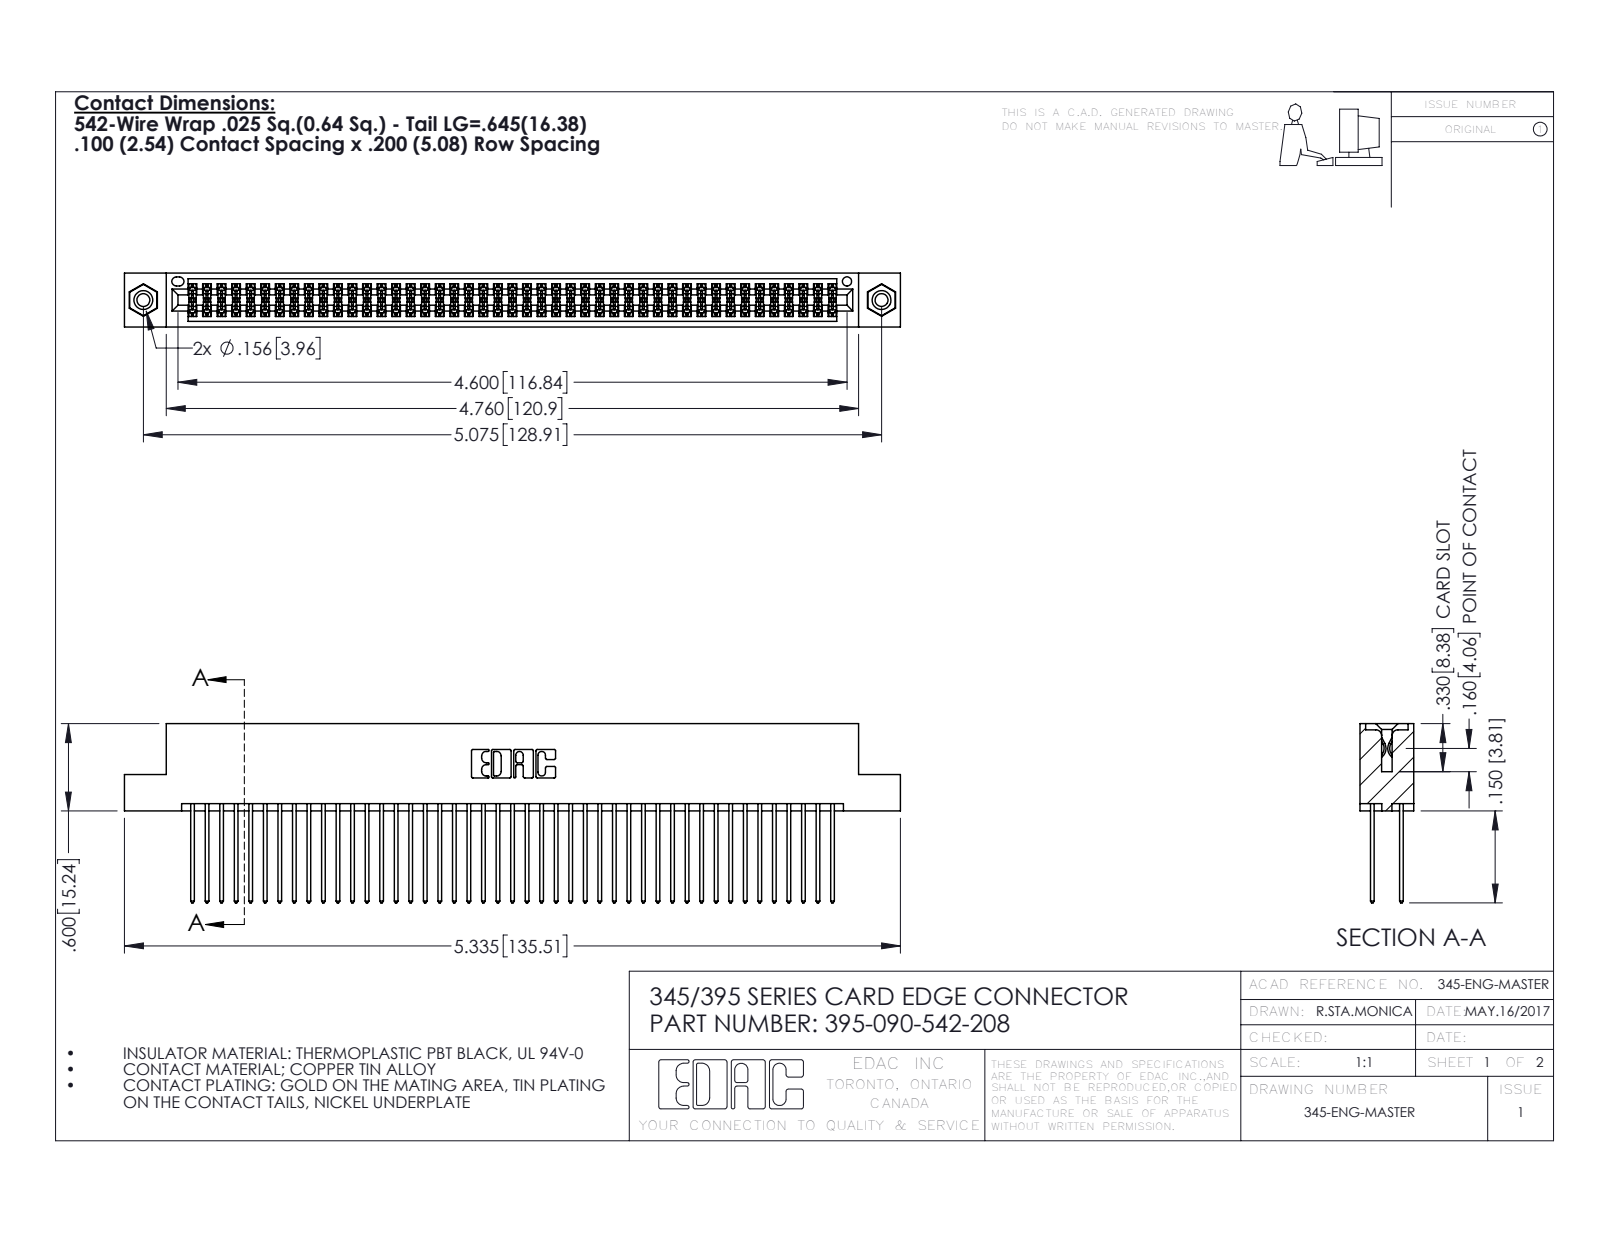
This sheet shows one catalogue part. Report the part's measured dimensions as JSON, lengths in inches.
{"part_name": "345 Part_Flush Mounting Lugs - 0.156 Dia-TI; 345-250-001_345-250-003-102; 395-090-542-208; 345-292-001_345-293-142", "step_written_by": "SolidWorks 2016 (CONFIG_CONTROL_DESIGN)", "units": "inches", "bodies": {"solids": 93, "faces": 4686, "planar": 3082, "cylindrical": 1588, "other": 16}, "overall_size": [5.335, 1.232, 0.37], "volume_in3": 0.83, "surface_area_in2": 34.32, "round_holes": [[0.089, 2], [0.125, 2], [0.156, 2], [0.064, 1]], "round_bosses_or_shafts": [[0.155, 2]], "partial_cylinders_radius": [[0.006, 135], [0.01, 90], [0.01, 22], [0.007, 6], [0.031, 6], [0.026, 3], [0.014, 2], [0.019, 2]], "face_to_face_distances": [0.072, 0.298, 0.2, 0.098, 0.272, 0.025, 0.225, 0.37, 0.175, 0.149], "hole_center_spacings": [0.27, 4.839, 5.075]}
